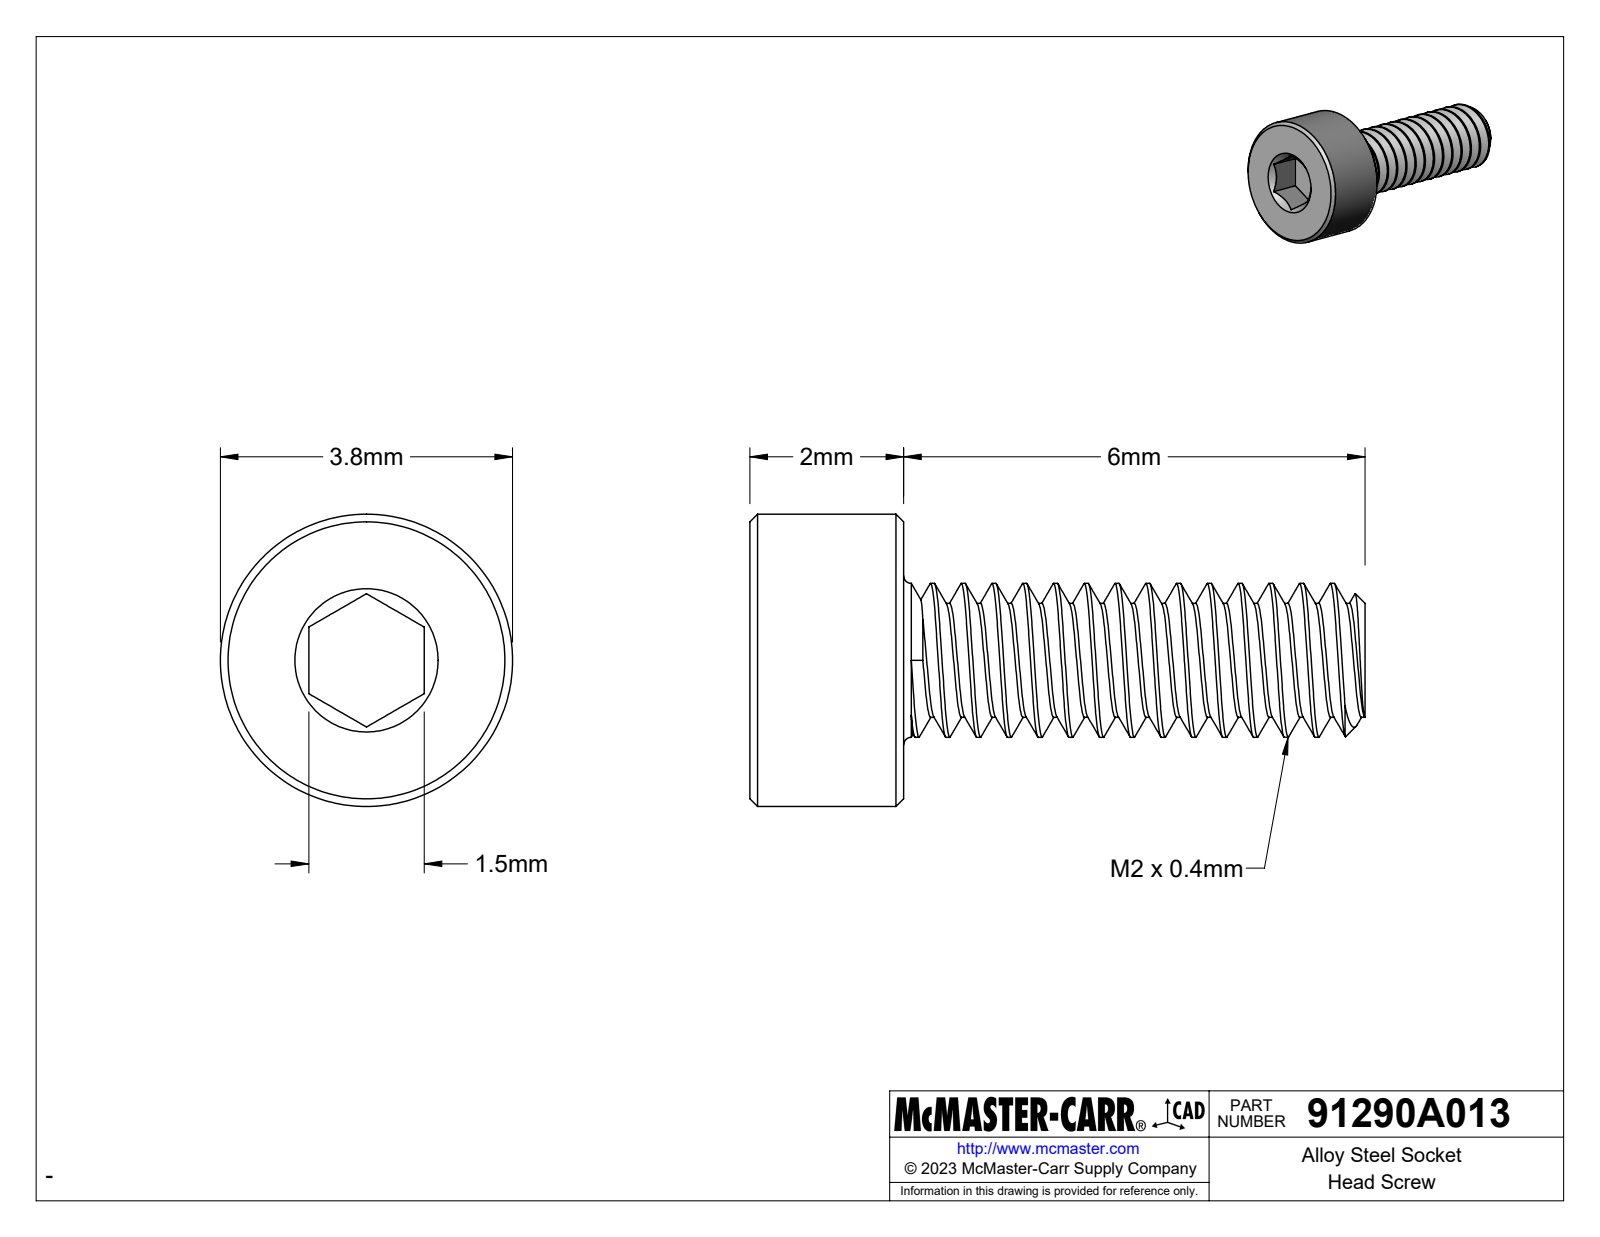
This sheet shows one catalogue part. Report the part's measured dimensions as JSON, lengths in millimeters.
{"part_name": "91290A013_Alloy Steel Socket Head Screw", "step_written_by": "SolidWorks 2017 (CONFIG_CONTROL_DESIGN)", "units": "millimeters", "bodies": {"solids": 1, "faces": 58, "planar": 10, "cylindrical": 31, "other": 17}, "overall_size": [8, 3.8, 3.8], "volume_mm3": 35, "surface_area_mm2": 105, "round_bosses_or_shafts": [[3.8, 1], [2, 1]], "face_to_face_distances": [2, 1, 1.5, 6, 7, 8]}
